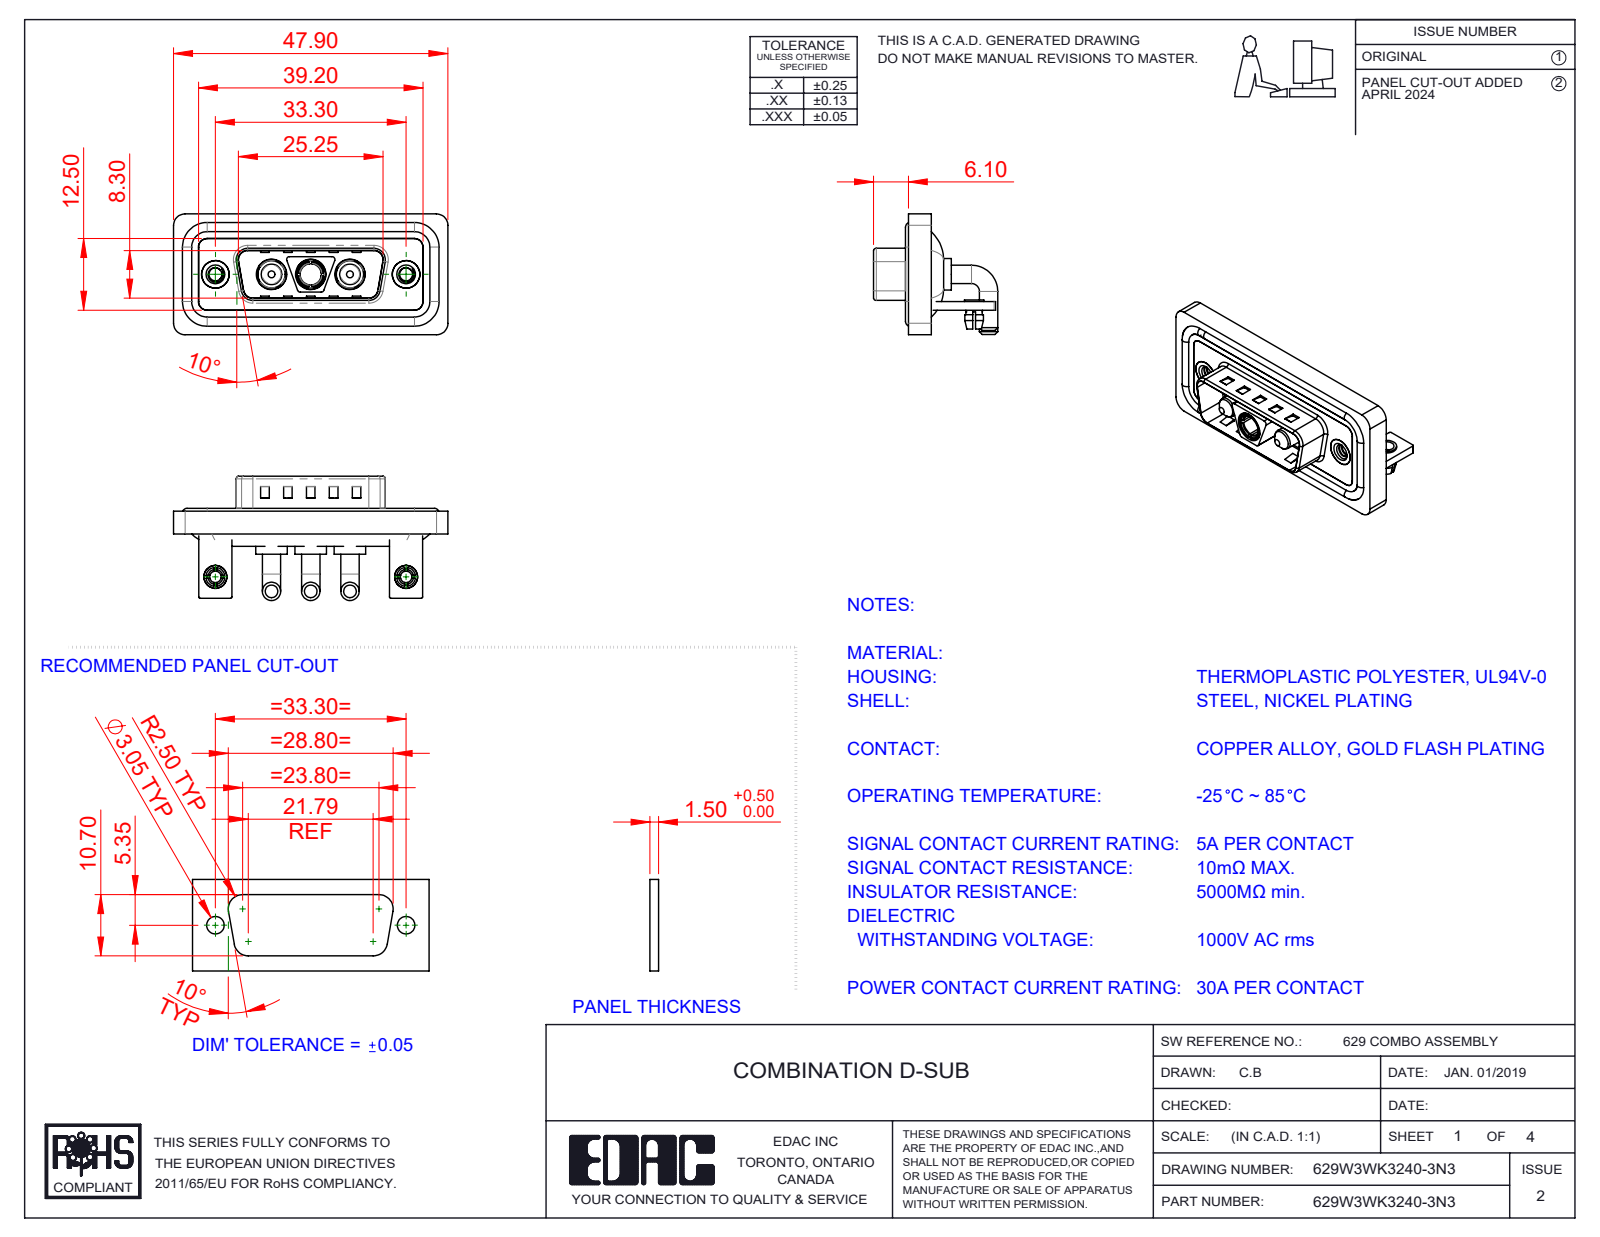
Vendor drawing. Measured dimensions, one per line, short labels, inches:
name: Power Pin_30A RA; 629Combo Stabilizer Bracket; 629Combo Board Lock; 629Combo Shell Front_15 Contacts (+6 more)
written by: SolidWorks 2023 (CONFIG_CONTROL_DESIGN)
unit: in
bodies: 17 solids, 753 faces (299 planar, 306 cylindrical, 148 other)
size: 1.886 × 0.854 × 0.831
volume: 0.383 in³; area: 15.92 in²
holes: 3× ⌀0.191, 3× ⌀0.209, 2× ⌀0.079, 2× ⌀0.089, 2× ⌀0.098, 2× ⌀0.126, 2× ⌀0.157, 2× ⌀0.189, 2× ⌀0.197, 1× ⌀0.146
bosses: 6× ⌀0.126, 4× ⌀0.063, 3× ⌀0.217, 3× ⌀0.205, 3× ⌀0.187, 3× ⌀0.148, 2× ⌀0.193, 2× ⌀0.157
rounds: 21× R0.079, 18× R0.059, 16× R0.01, 13× R0.02, 8× R0.063, 4× R0.024, 4× R0.026, 4× R0.035
face distances: 0.016, 0.059, 0.031, 0.114, 0.043, 0.083, 0.146, 0.063, 0.047, 0.177
hole spacings: 0.27, 0.386, 0.656, 0.925, 1.311, 0.539
